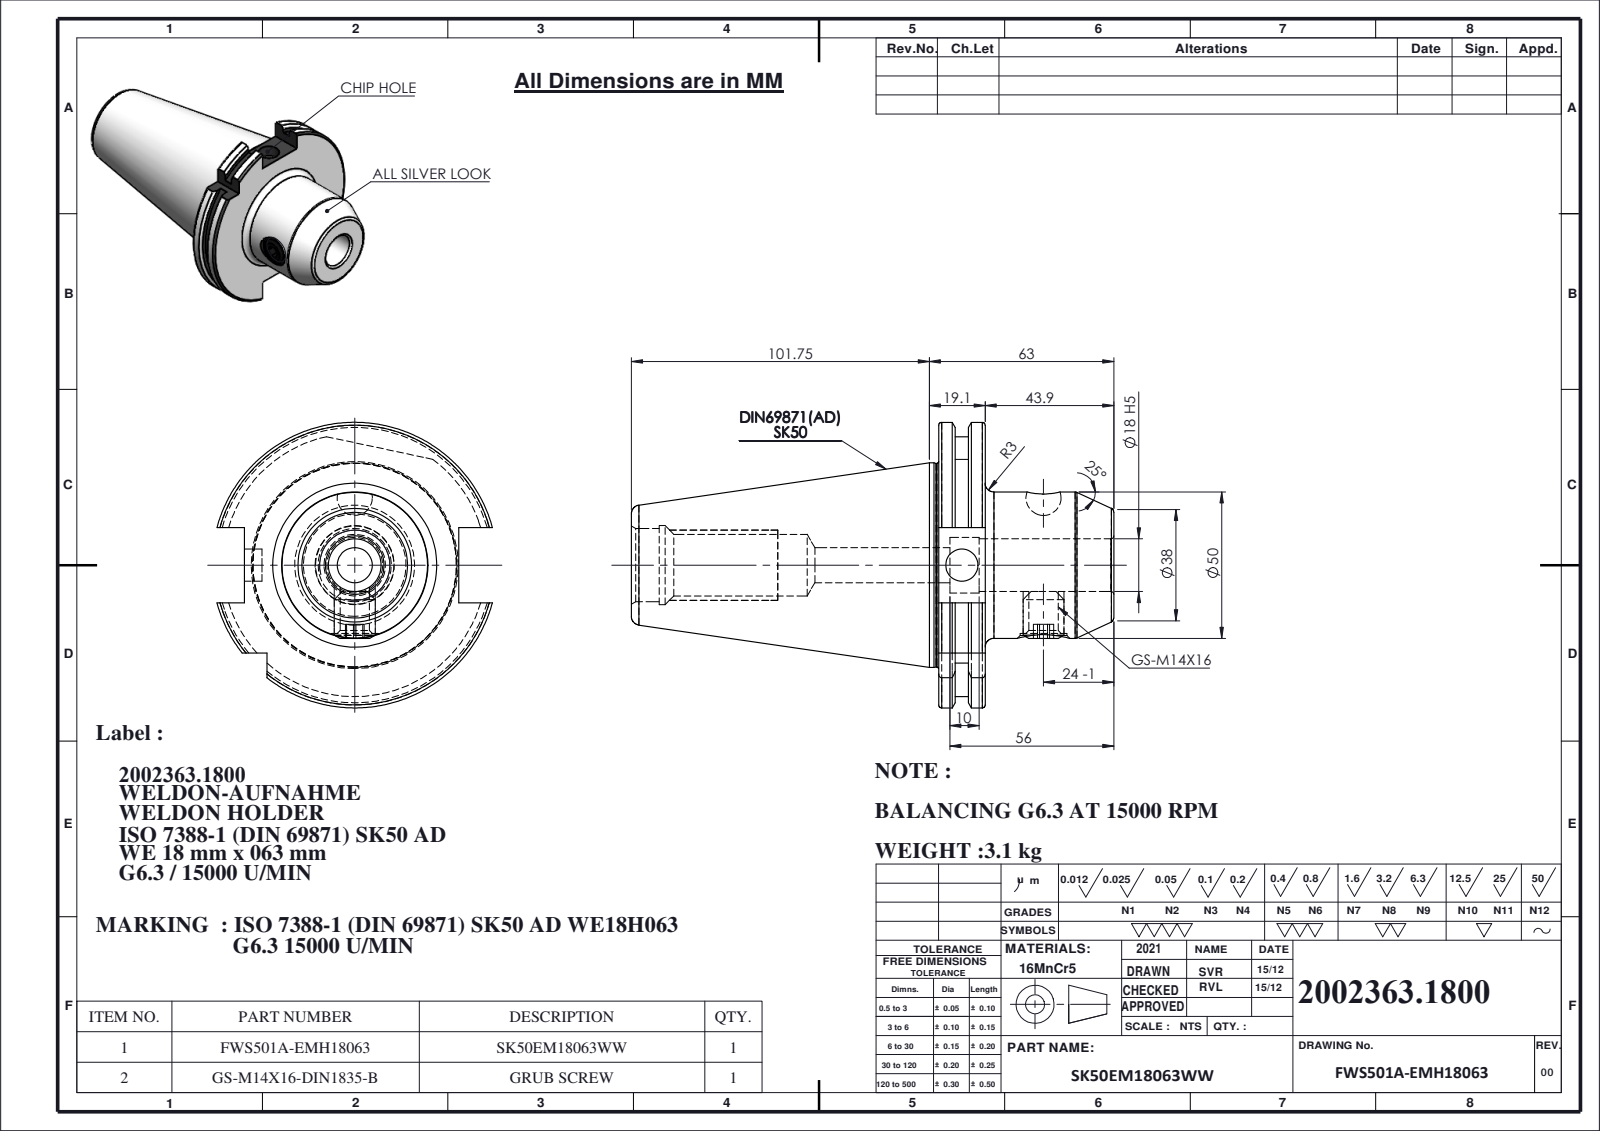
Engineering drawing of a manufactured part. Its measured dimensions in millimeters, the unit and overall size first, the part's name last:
Units: millimetres
Overall size (bounding box): 164.75 × 97.5 × 94.05
Round holes (diameter × count): ⌀10 ×1, ⌀11 ×1, ⌀12 ×1, ⌀16 ×1, ⌀18 ×1, ⌀19 ×1, ⌀21 ×1, ⌀25 ×1, ⌀27 ×1
Round bosses / shafts (diameter × count): ⌀69.85 ×1, ⌀69.45 ×1, ⌀50 ×1, ⌀14 ×1
Partial cylindrical surfaces — rounded edges, fillets, slot ends (radius × count): R44.9 ×1, R48.75 ×1
Main face-to-face distances: 15.9, 59.8, 43.9, 5.65, 10.25, 54.15, 10.14, 4.49, 5.76, 49.66
Volume: 400 416 mm³ · Surface area: 52 673 mm²
Bodies: 2 solids, 125 faces (33 planar, 39 cylindrical, 53 other)
Part name (STEP PRODUCT): GS-M14X16-DIN1835-B_ISO 4026 - M12 x 12-N; SK50EM18063WW; 91506-WE118063; GS-M14X16-DIN1835-B
STEP written by: SolidWorks 2018 (CONFIG_CONTROL_DESIGN)
